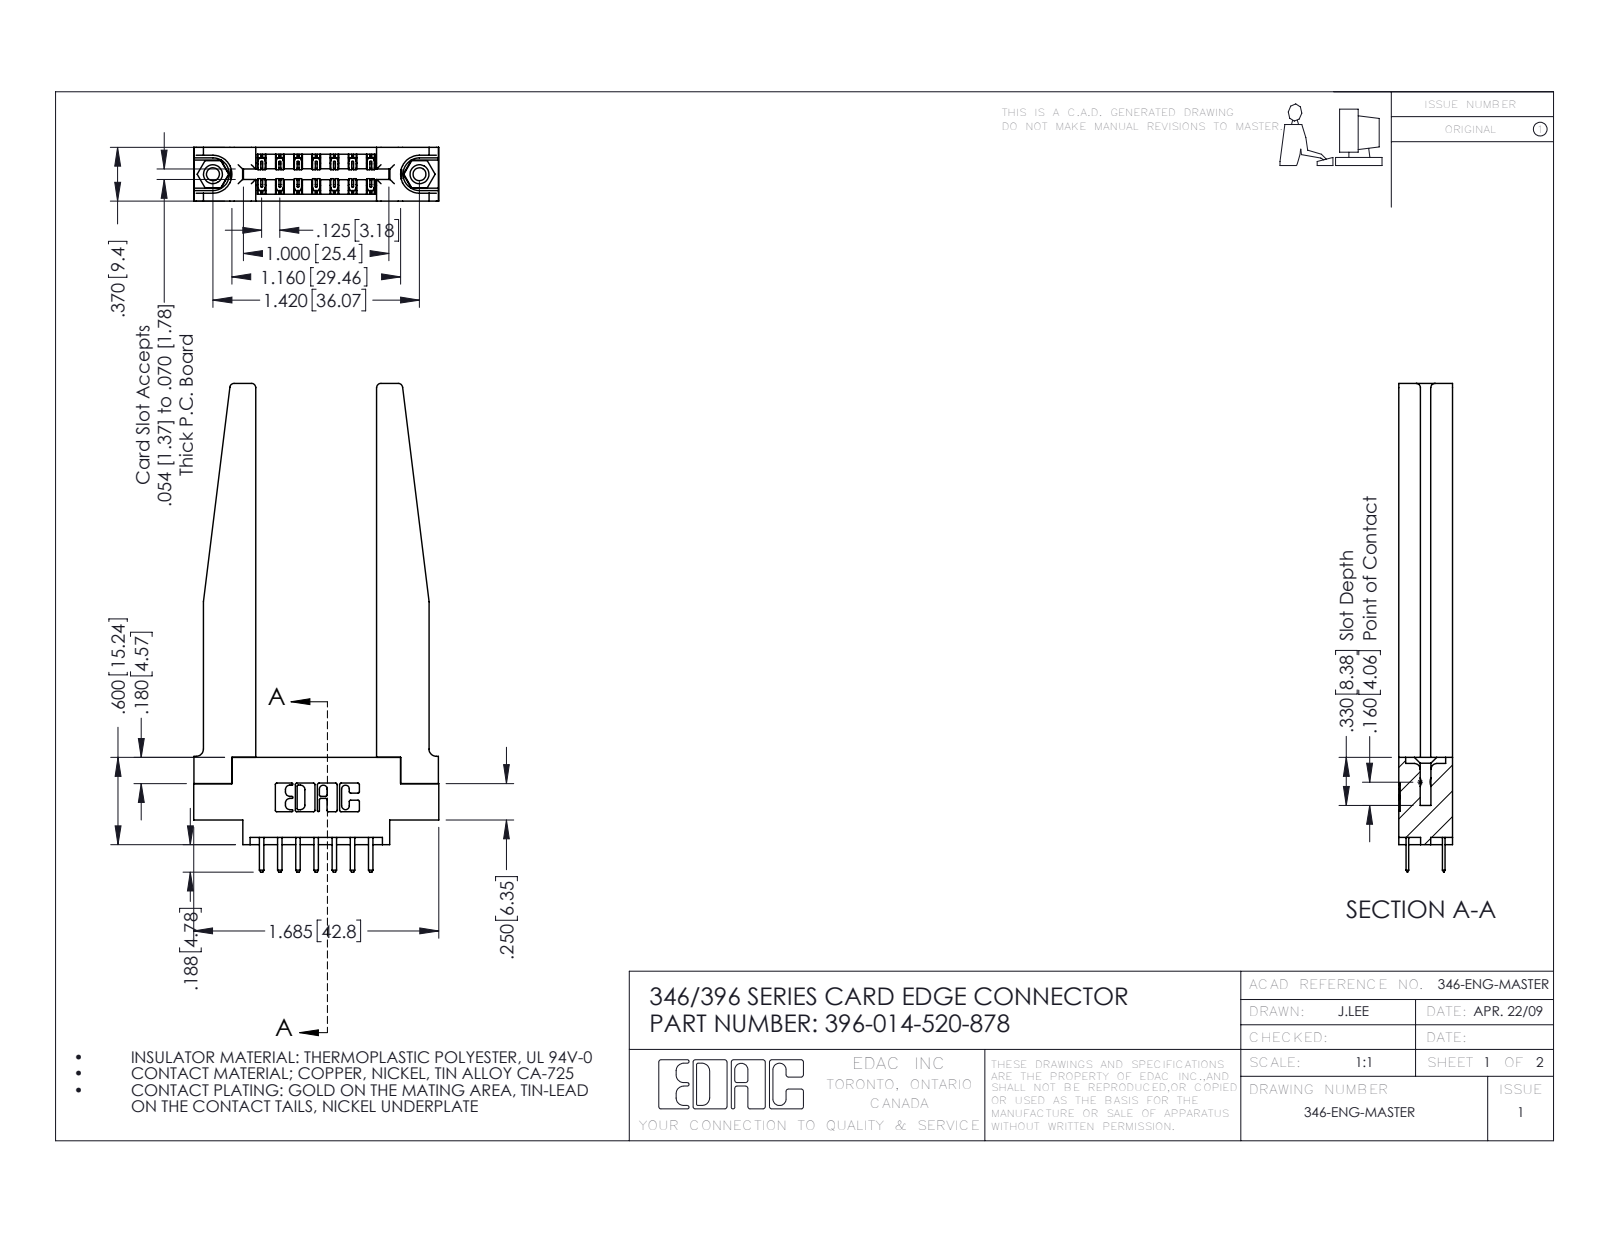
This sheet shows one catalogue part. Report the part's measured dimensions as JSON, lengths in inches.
{"part_name": "396-014-520-878; 346 Part_0.170 Offset - 0.156 Dia-TH; 346-220-078_345-220-078; 345-292-001_345-293-120 (+1 more)", "step_written_by": "SolidWorks 2016 (CONFIG_CONTROL_DESIGN)", "units": "inches", "bodies": {"solids": 19, "faces": 1144, "planar": 740, "cylindrical": 352, "other": 52}, "overall_size": [3.358, 1.685, 0.37], "volume_in3": 0.65, "surface_area_in2": 17.51, "round_holes": [[0.089, 2], [0.125, 2], [0.156, 2], [0.064, 1]], "round_bosses_or_shafts": [[0.155, 2]], "partial_cylinders_radius": [[0.01, 22], [0.006, 21], [0.01, 18], [0.03, 8], [0.007, 6], [0.031, 6], [0.026, 3], [0.014, 2]], "face_to_face_distances": [0.37, 0.15, 0.22, 0.25, 0.831, 0.148, 0.072, 0.102, 0.048, 0.322], "hole_center_spacings": [0.246, 1.217, 1.42]}
